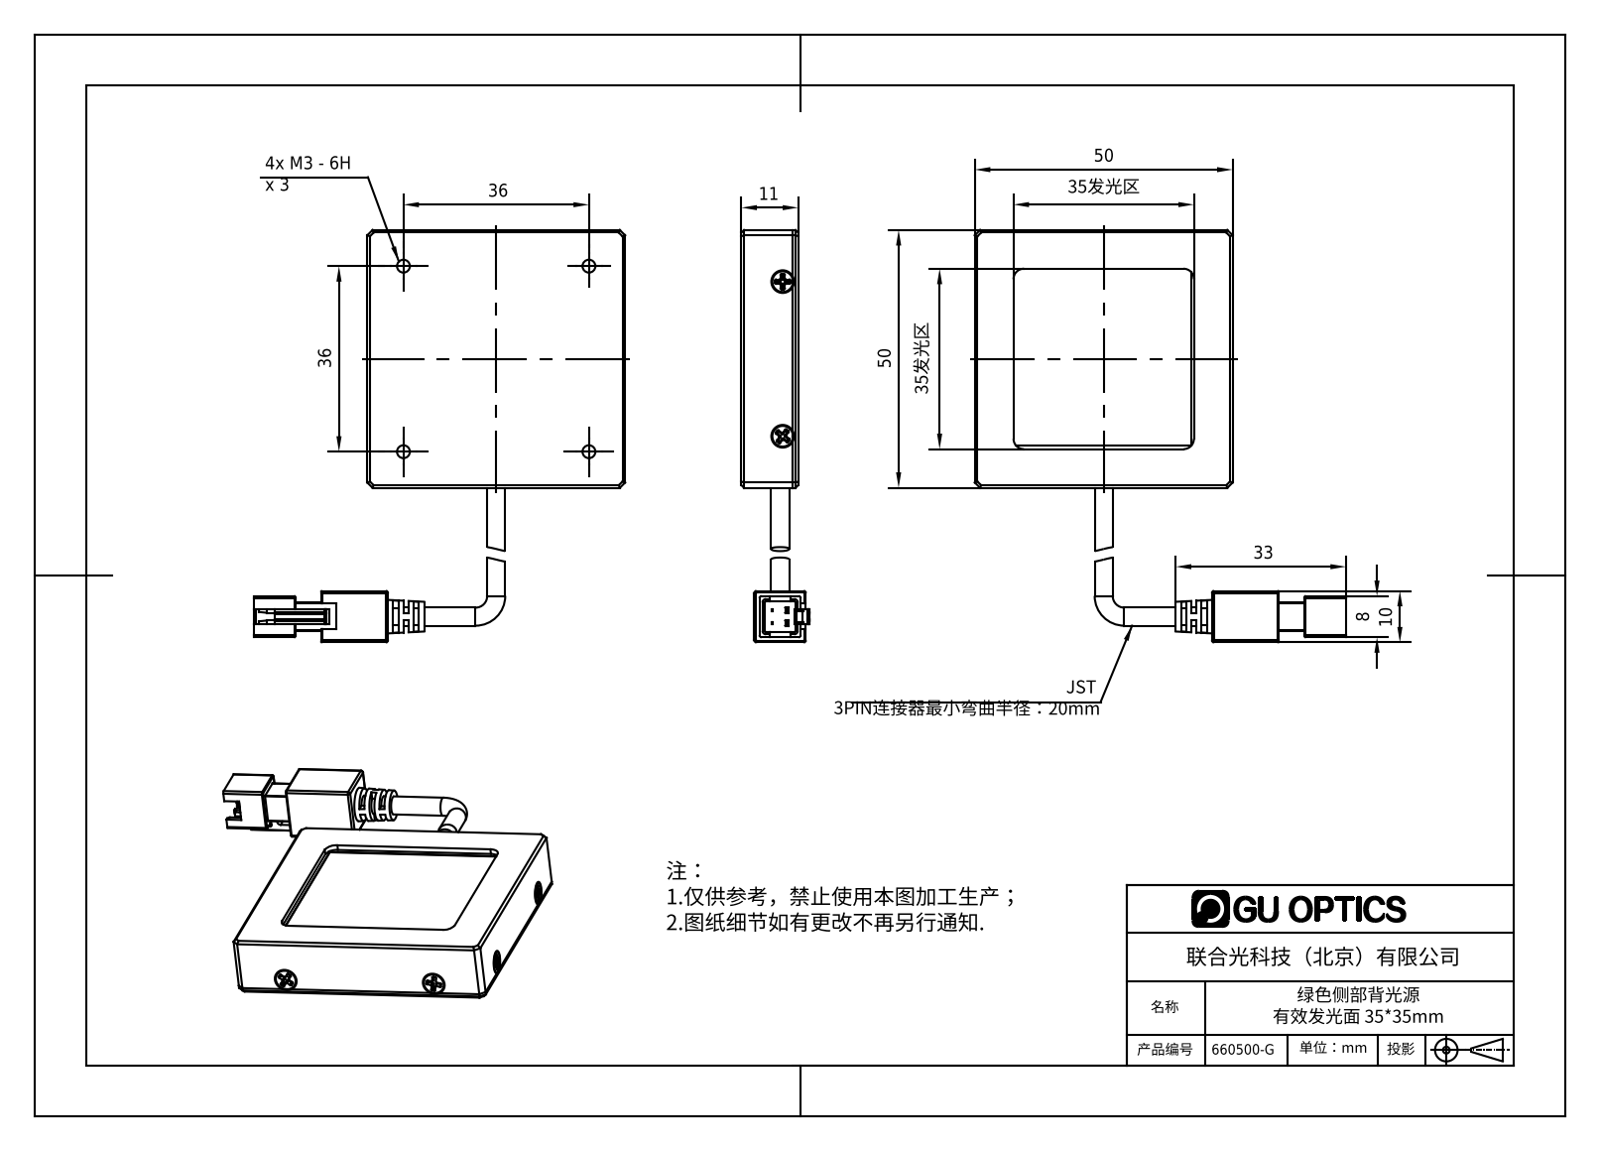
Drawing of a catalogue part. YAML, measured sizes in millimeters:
part_name: "660500-R"
step_written_by: "SolidWorks 2016 (AUTOMOTIVE_DESIGN)"
units: millimeters
bodies: {solids: 37, faces: 955, planar: 540, cylindrical: 232, other: 183}
overall_size: [80.2, 72, 13.2]
volume: 23999
surface_area: 35401
round_holes:
  - {diameter: 1.6, count: 4}
  - {diameter: 2.4, count: 4}
  - {diameter: 2.5, count: 4}
  - {diameter: 3.6, count: 1}
round_bosses_or_shafts:
  - {diameter: 2, count: 4}
  - {diameter: 3.5, count: 2}
partial_cylinders:
  - {radius: 0.2, count: 109}
  - {radius: 0.1, count: 15}
  - {radius: 0.4, count: 12}
  - {radius: 1, count: 7}
  - {radius: 2, count: 4}
  - {radius: 0.3, count: 1}
  - {radius: 0.68, count: 1}
  - {radius: 1.4, count: 1}
face_to_face_distances: [4.2, 1, 5.5, 4.1, 1.2, 4.5, 4.3, 1.1, 5.3, 4]
hole_center_spacings: [36, 15.01, 30, 50.91]
